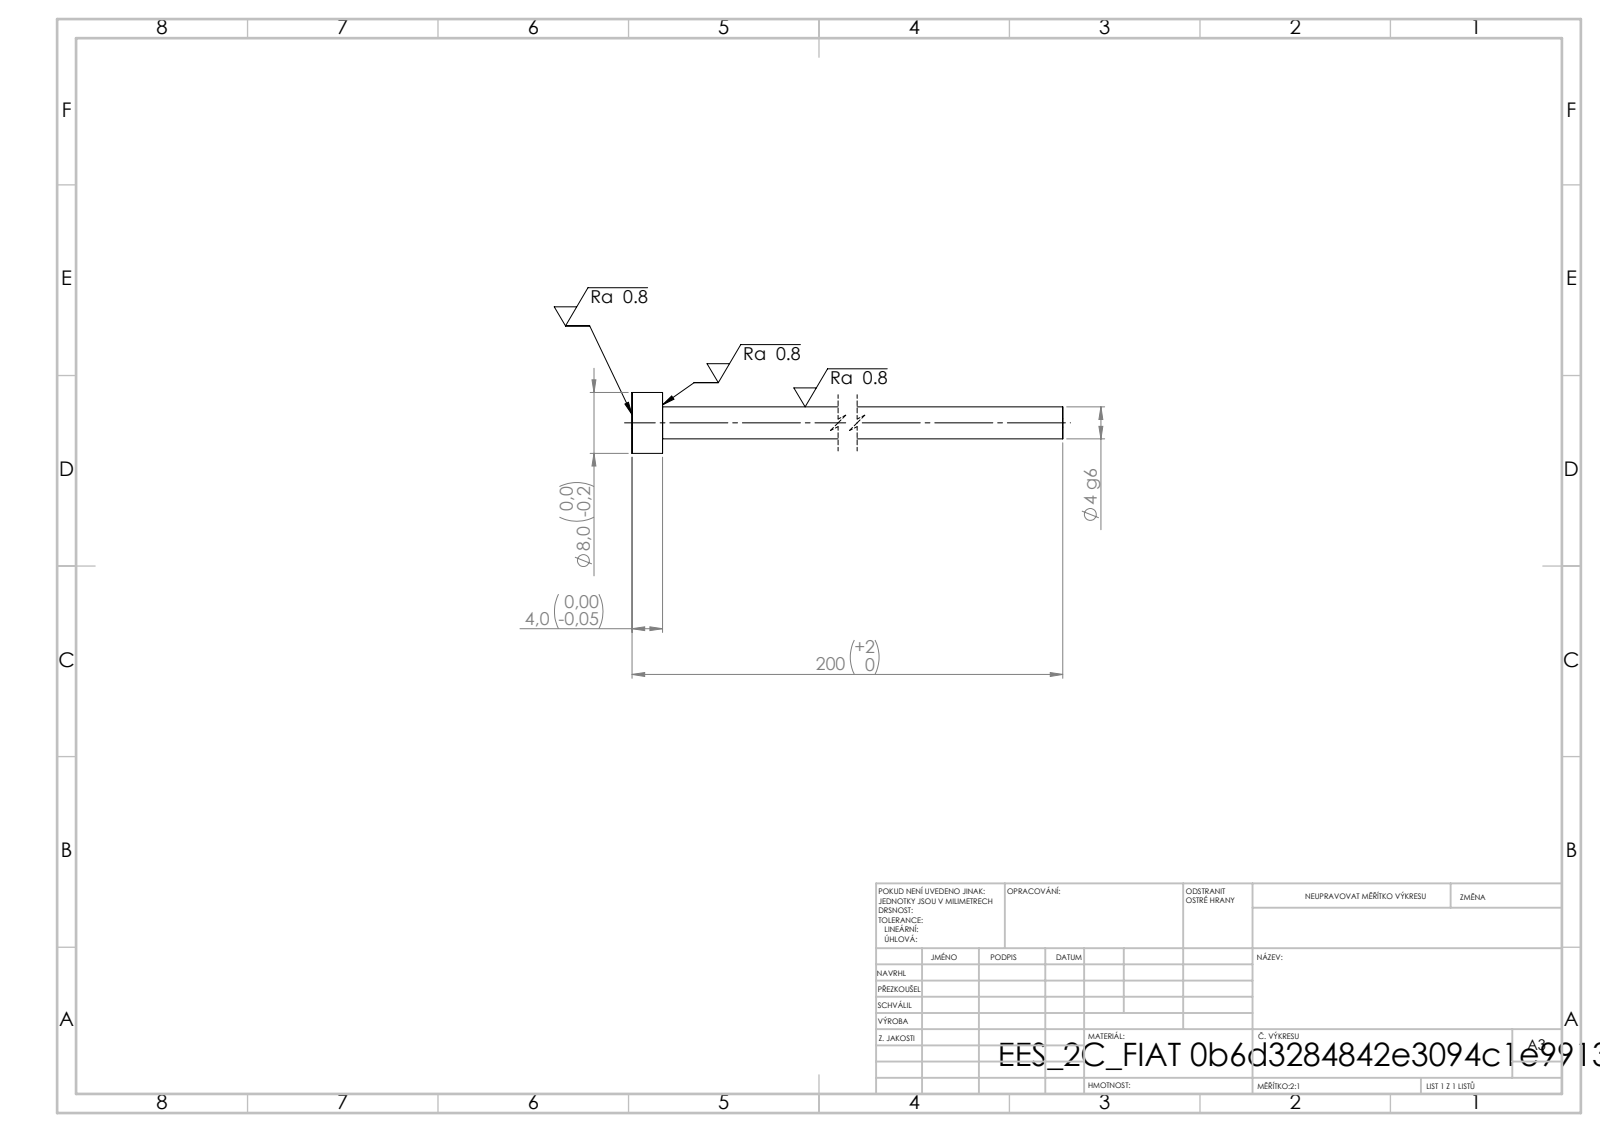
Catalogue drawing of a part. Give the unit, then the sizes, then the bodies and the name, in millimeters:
Units: millimetres
Overall size (bounding box): 200 × 8 × 8
Round bosses / shafts (diameter × count): ⌀8 ×1, ⌀4.2 ×1
Main face-to-face distances: 4, 200, 196
Volume: 2 917 mm³ · Surface area: 2 787 mm²
Bodies: 1 solid, 7 faces (3 planar, 4 cylindrical, 0 other)
STEP written by: SolidWorks 2019 (CONFIG_CONTROL_DESIGN)
